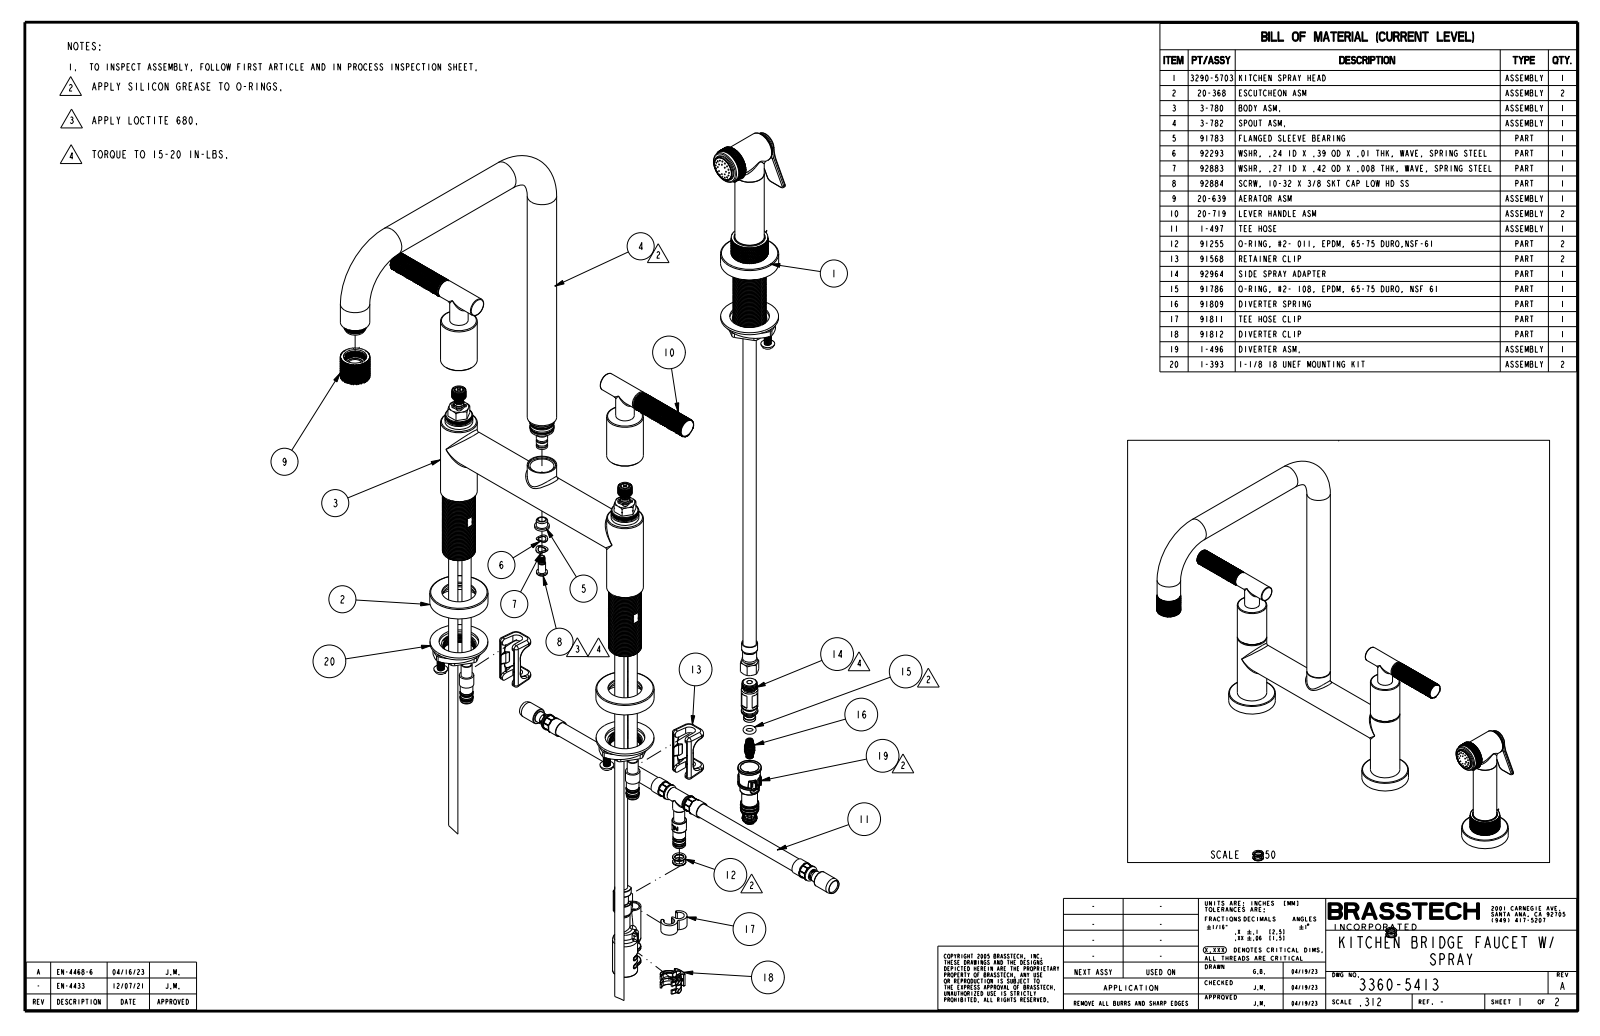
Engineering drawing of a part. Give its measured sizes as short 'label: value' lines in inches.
name: 3360-5413
written by: CREO PARAMETRIC BY PTC INC, 2019352 (CONFIG_CONTROL_DESIGN)
unit: in
bodies: 4 solids, 25873 faces (176 planar, 5164 cylindrical, 20533 other)
size: 17.99 × 15.045 × 10.89
volume: 48.91 in³; area: 206.5 in²
holes: 1× ⌀0.525
bosses: 4× ⌀1.25, 4× ⌀1, 3× ⌀1.98, 3× ⌀0.63, 2× ⌀0.51, 1× ⌀1.175, 1× ⌀1.1, 1× ⌀1.023
rounds: 10× R0.04, 2× R0.16, 1× R0.332, 1× R0.385, 1× R0.75, 1× R2
face distances: 0.425, 4.942, 4.517, 3.857, 1.085, 0.66, 0.021, 0.13, 1.106, 3.525
